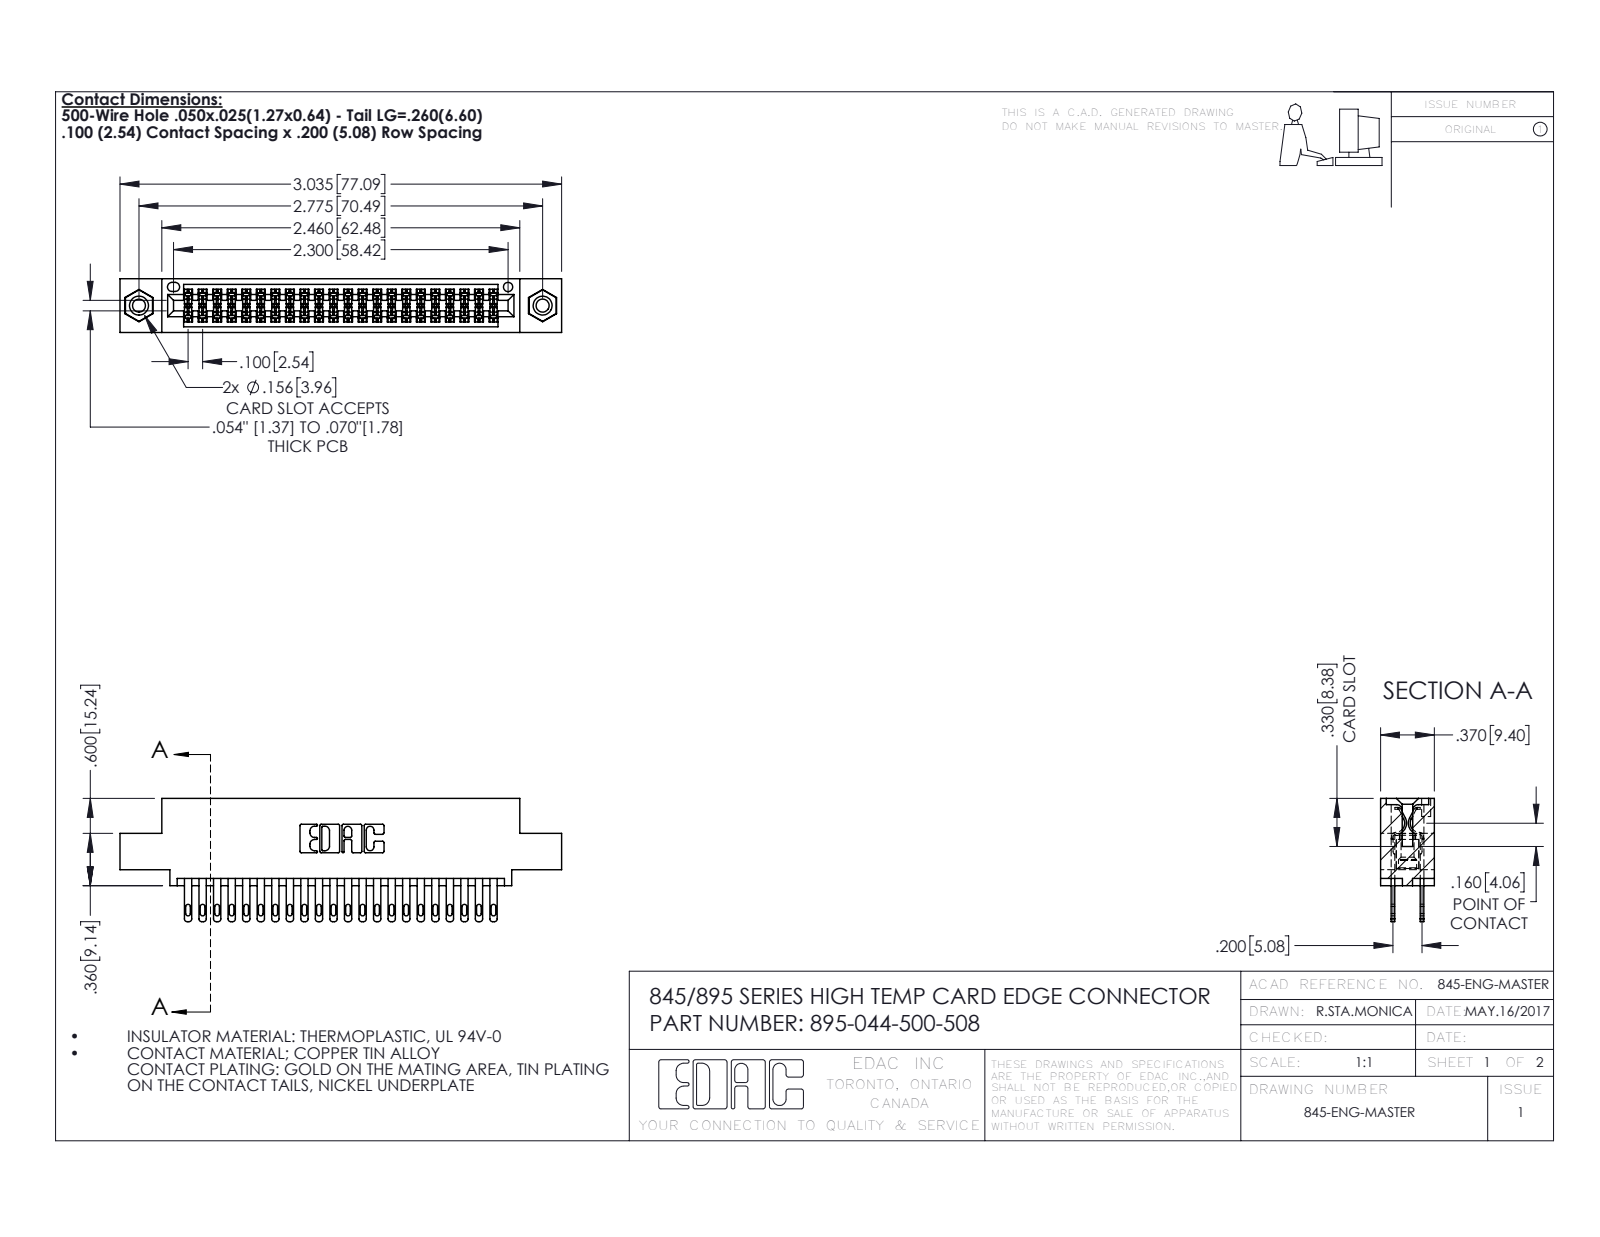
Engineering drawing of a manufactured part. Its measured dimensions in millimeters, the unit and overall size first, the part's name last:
Units: millimetres
Overall size (bounding box): 77.1 × 21.5 × 9.4
Round holes (diameter × count): ⌀2.3 ×2, ⌀3.2 ×2, ⌀4 ×2, ⌀1.6 ×1
Round bosses / shafts (diameter × count): ⌀3.9 ×2
Partial cylindrical surfaces — rounded edges, fillets, slot ends (radius × count): R0.2 ×66, R0.4 ×44, R0.5 ×44, R0.3 ×22, R0.2 ×6, R0.8 ×6, R0.7 ×3, R0.4 ×2
Main face-to-face distances: 1.8, 7.6, 5.1, 2.5, 6.9, 0.6, 9.4, 5.7, 4.4, 3.8
Hole centre spacings: 6.9, 64.5, 70.5
Volume: 7 360 mm³ · Surface area: 11 050 mm²
Bodies: 47 solids, 2214 faces (1304 planar, 894 cylindrical, 16 other)
Part name (STEP PRODUCT): 895-044-500-508; 845 Part_0.110 Offset - 0.156 Dia-TI; 345-250-001_345-250-003-102; 345-292-001_345-293-100
STEP written by: SolidWorks 2020 (CONFIG_CONTROL_DESIGN)
